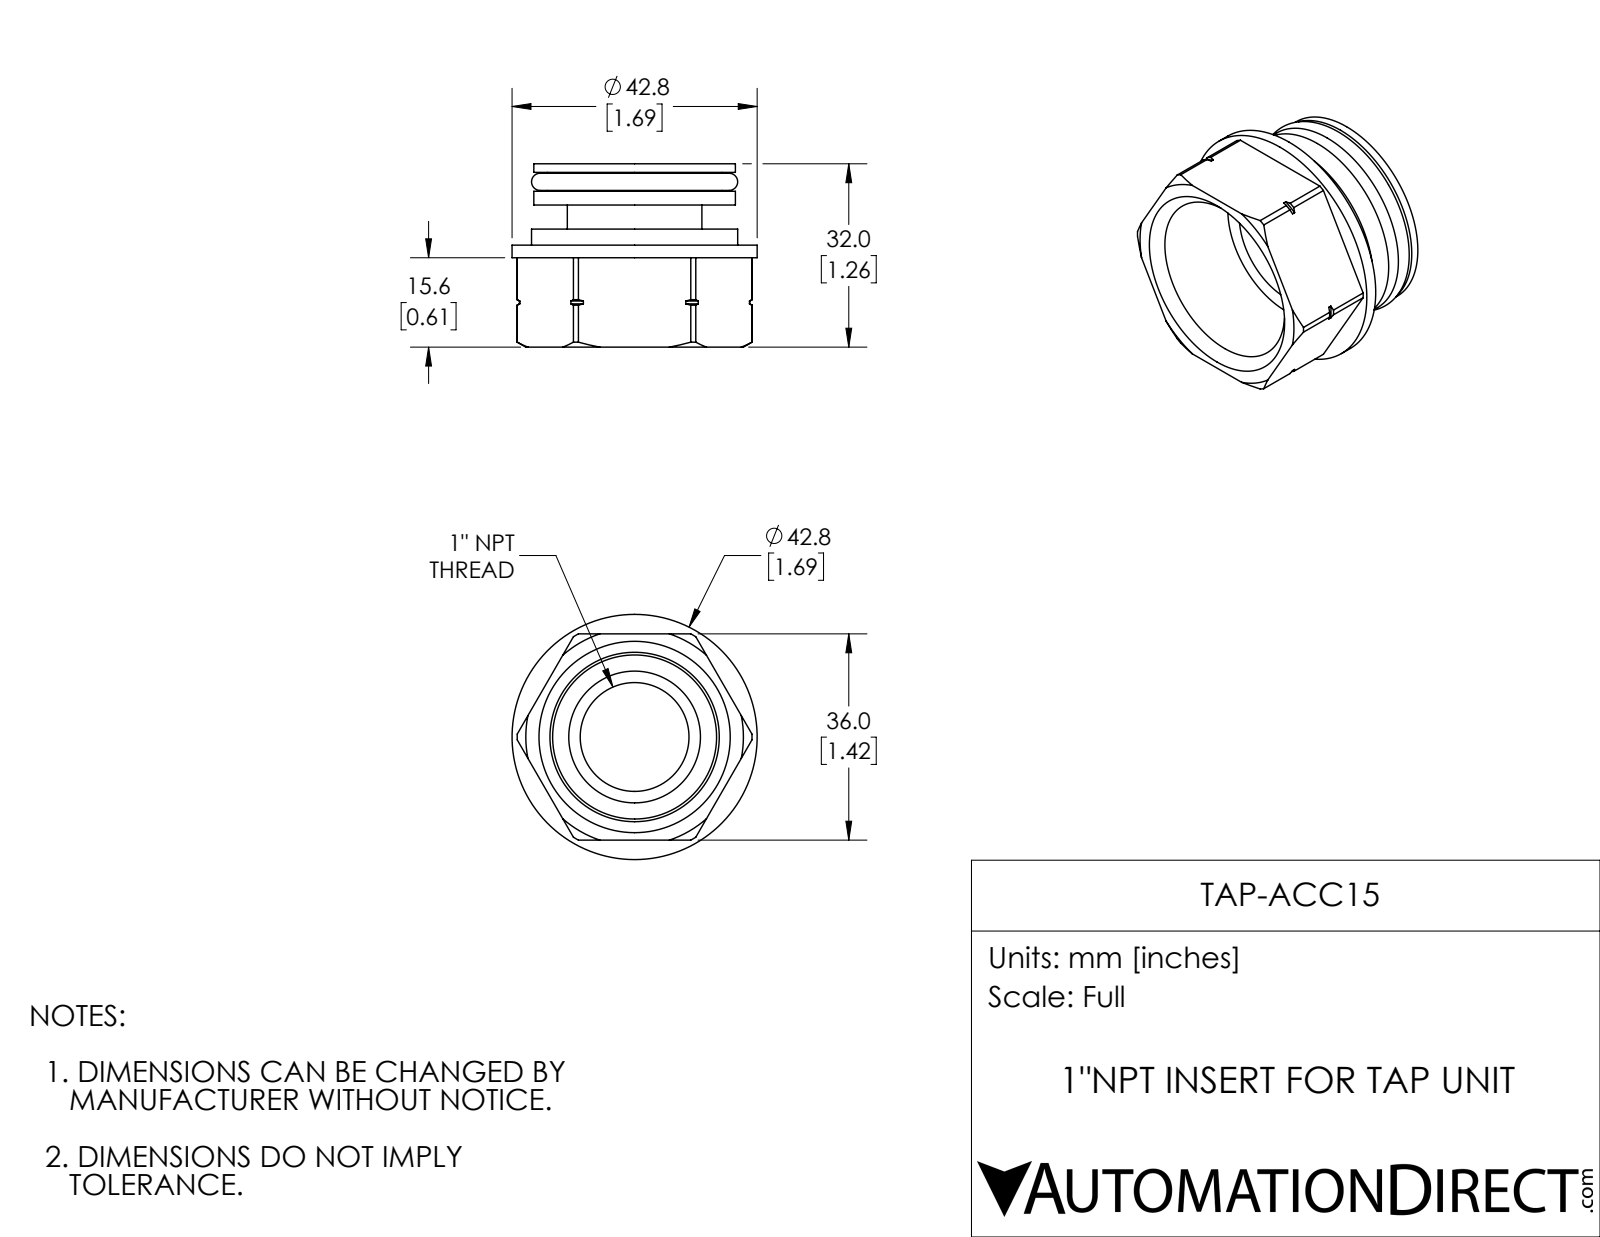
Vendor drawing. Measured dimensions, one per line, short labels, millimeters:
name: TAP-ACC15
written by: SolidWorks 2017 (AUTOMOTIVE_DESIGN)
unit: mm
bodies: 1 solid, 83 faces (15 planar, 36 cylindrical, 32 other)
size: 42.8 × 42.8 × 32
volume: 15 400 mm³; area: 10 300 mm²
holes: 1× ⌀19, 1× ⌀26
bosses: 1× ⌀42.8, 1× ⌀36, 1× ⌀35.2, 1× ⌀30.5, 1× ⌀23.5
rounds: 1× R20.1, 1× R20.5
face distances: 36, 4.2, 11.4, 7.2, 2.8, 7, 14.2, 2.2, 5, 9.2
